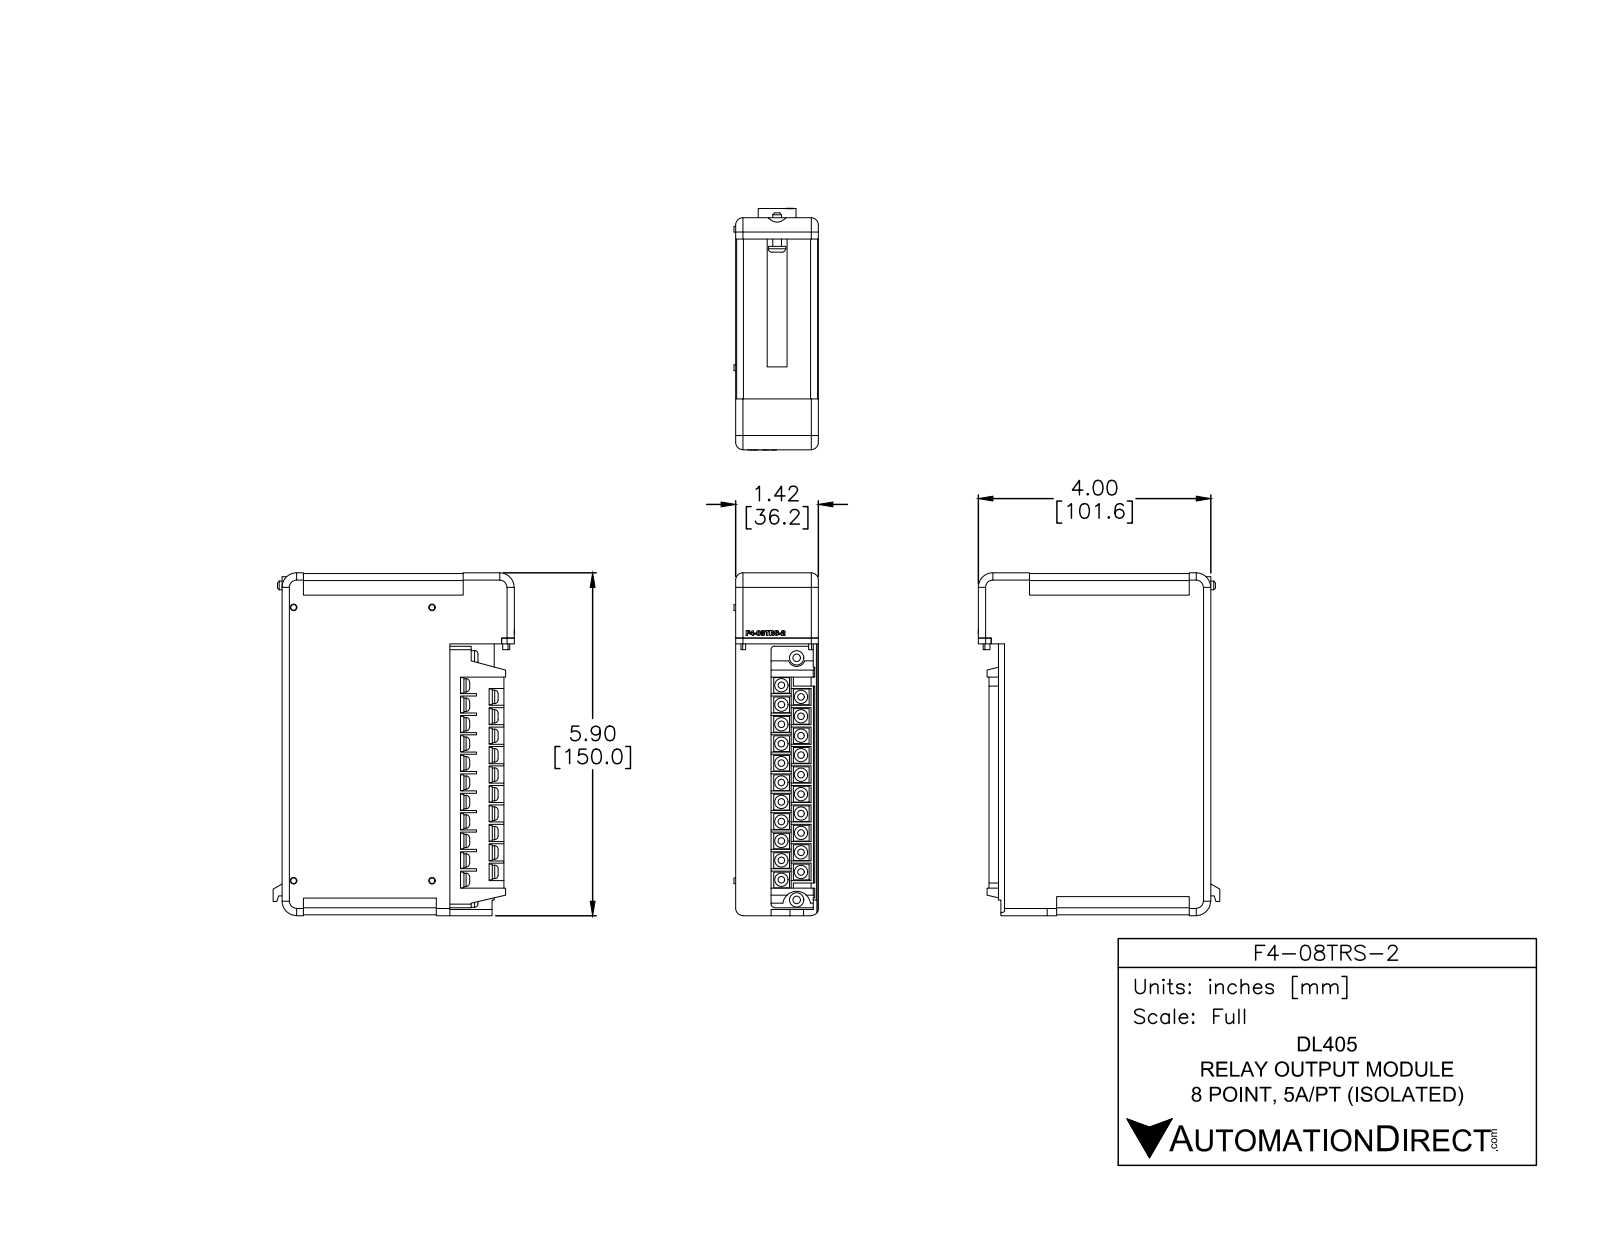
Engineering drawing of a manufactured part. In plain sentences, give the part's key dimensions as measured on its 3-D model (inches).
The part is named "F4-08TRS-2". Its 3-D file was written by "SolidWorks 2014 (AUTOMOTIVE_DESIGN)". It is 16 solids with 637 faces: 425 planar, 86 cylindrical and 126 other. Overall it measures 5.905 by 4.156 by 1.455 inches. Its volume is 27.51 cubic inches and its surface area 86.83 square inches. Round bosses or shafts: 21 of diameter 0.23, 2 of diameter 0.25, 1 of diameter 0.3, 1 of diameter 0.15. Partial cylindrical surfaces (rounded edges, fillets, slot ends): 8 of radius 0.125, 4 of radius 0.12, 3 of radius 0.25, 2 of radius 0.015, 2 of radius 0.03, 2 of radius 0.06, 1 of radius 0.149, 1 of radius 0.151. The main face-to-face distances are 1.425, 0.015, 2.89, 5.875, 1.41, 0.47, 0.2, 0.955, 5.89, 1.21.
